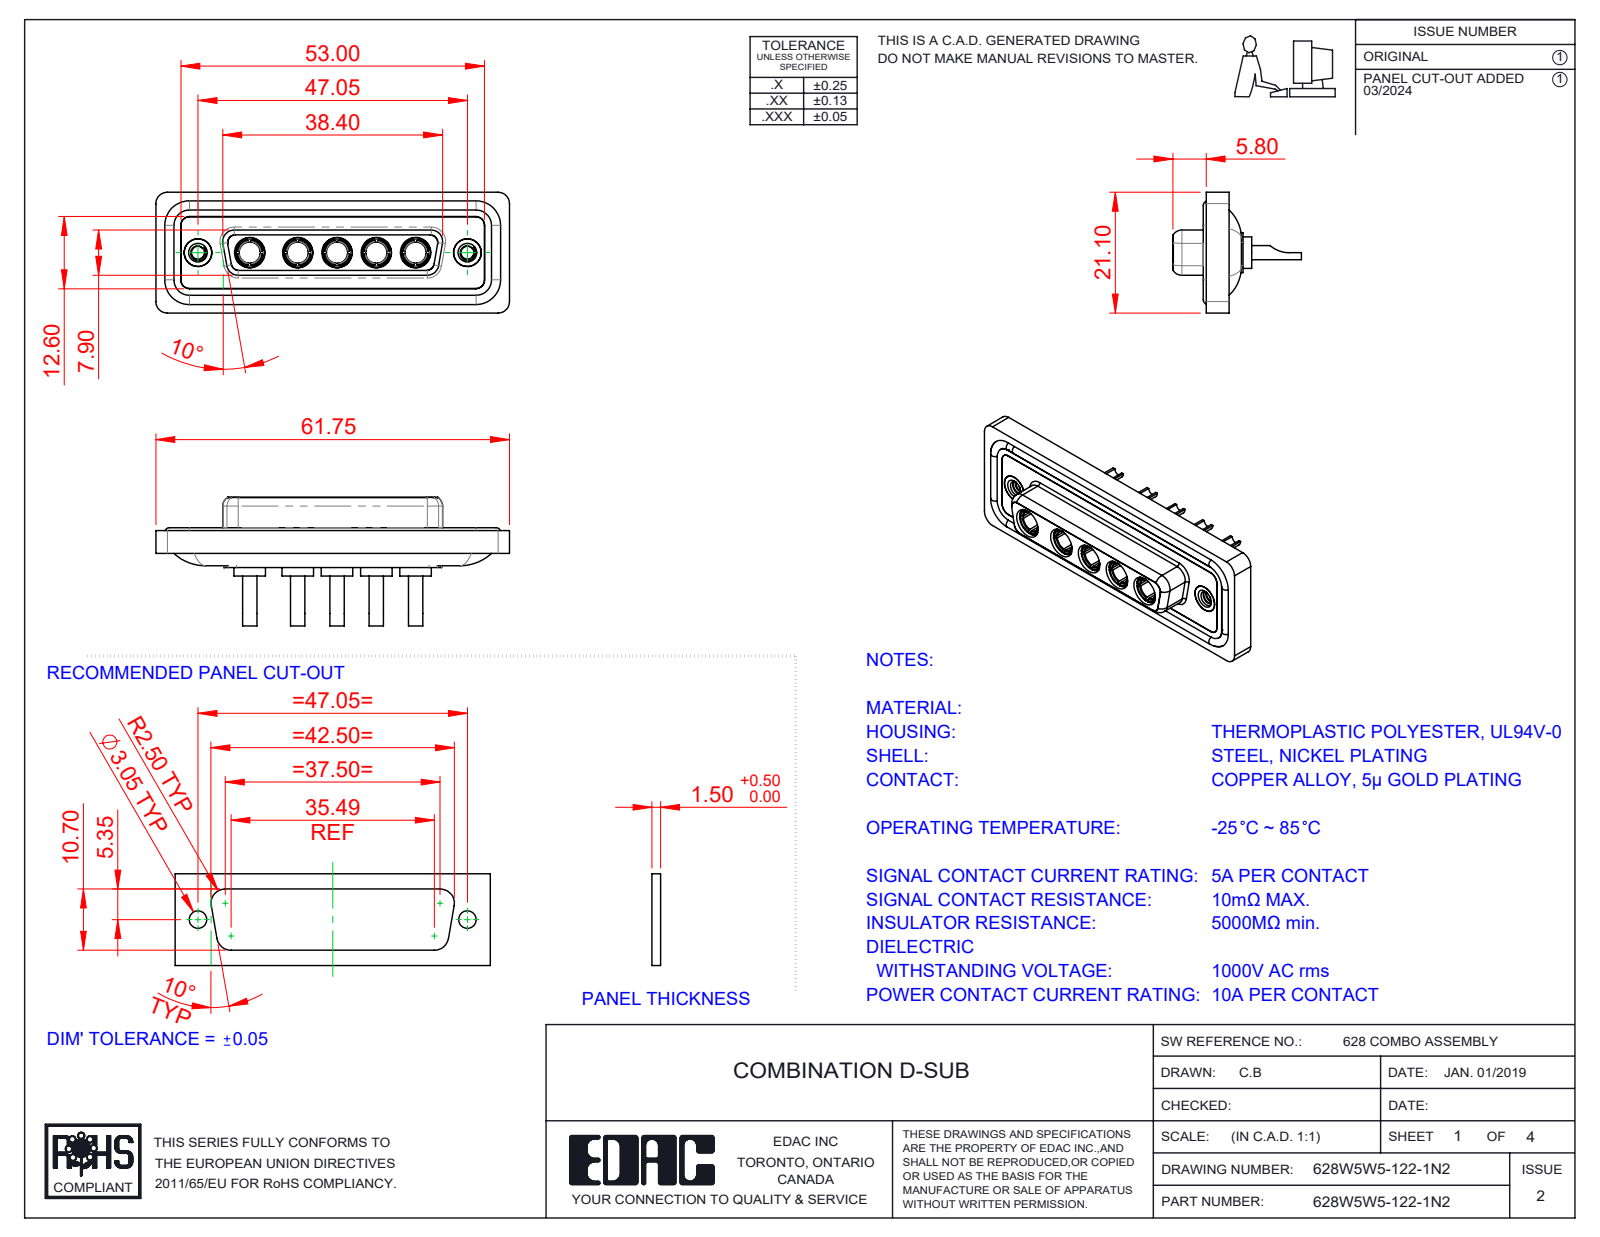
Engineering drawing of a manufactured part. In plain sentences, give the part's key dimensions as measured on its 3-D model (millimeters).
The part is named "628Combo Threaded Rivet_2; 628Combo Waterproof Housing_25 Contacts; Power Socket_10A SC; 628Combo Shell Front_25 Contacts (+3 more)". Its 3-D file was written by "SolidWorks 2023 (CONFIG_CONTROL_DESIGN)". It is 17 solids with 781 faces: 260 planar, 318 cylindrical and 203 other. Overall it measures 61.75 by 22.45 by 21.1 millimeters. Its volume is 8 159 cubic millimeters and its surface area 13 654 square millimeters. Round holes: 7 of diameter 4.85, 5 of diameter 1.7, 5 of diameter 3.7, 5 of diameter 5.3, 2 of diameter 2.26, 2 of diameter 4, 2 of diameter 4.05, 2 of diameter 5. Round bosses or shafts: 5 of diameter 5.5, 5 of diameter 5.2, 5 of diameter 4.96, 5 of diameter 4.75, 5 of diameter 3.75, 5 of diameter 2.5, 4 of diameter 1.6, 2 of diameter 4.95. Partial cylindrical surfaces (rounded edges, fillets, slot ends): 22 of radius 1.5, 18 of radius 2, 8 of radius 1.35, 8 of radius 1.6, 5 of radius 2.1, 4 of radius 0.25, 4 of radius 0.5, 4 of radius 0.6. The main face-to-face distances are 0.4, 1.8, 7.45, 5.65, 0.5, 7.05, 6.6, 1.6, 1.1, 2.9. The hole center spacings are 6.86, 9.04, 13.72, 38.01, 8.39, 15.25, 15.9, 17.43.
